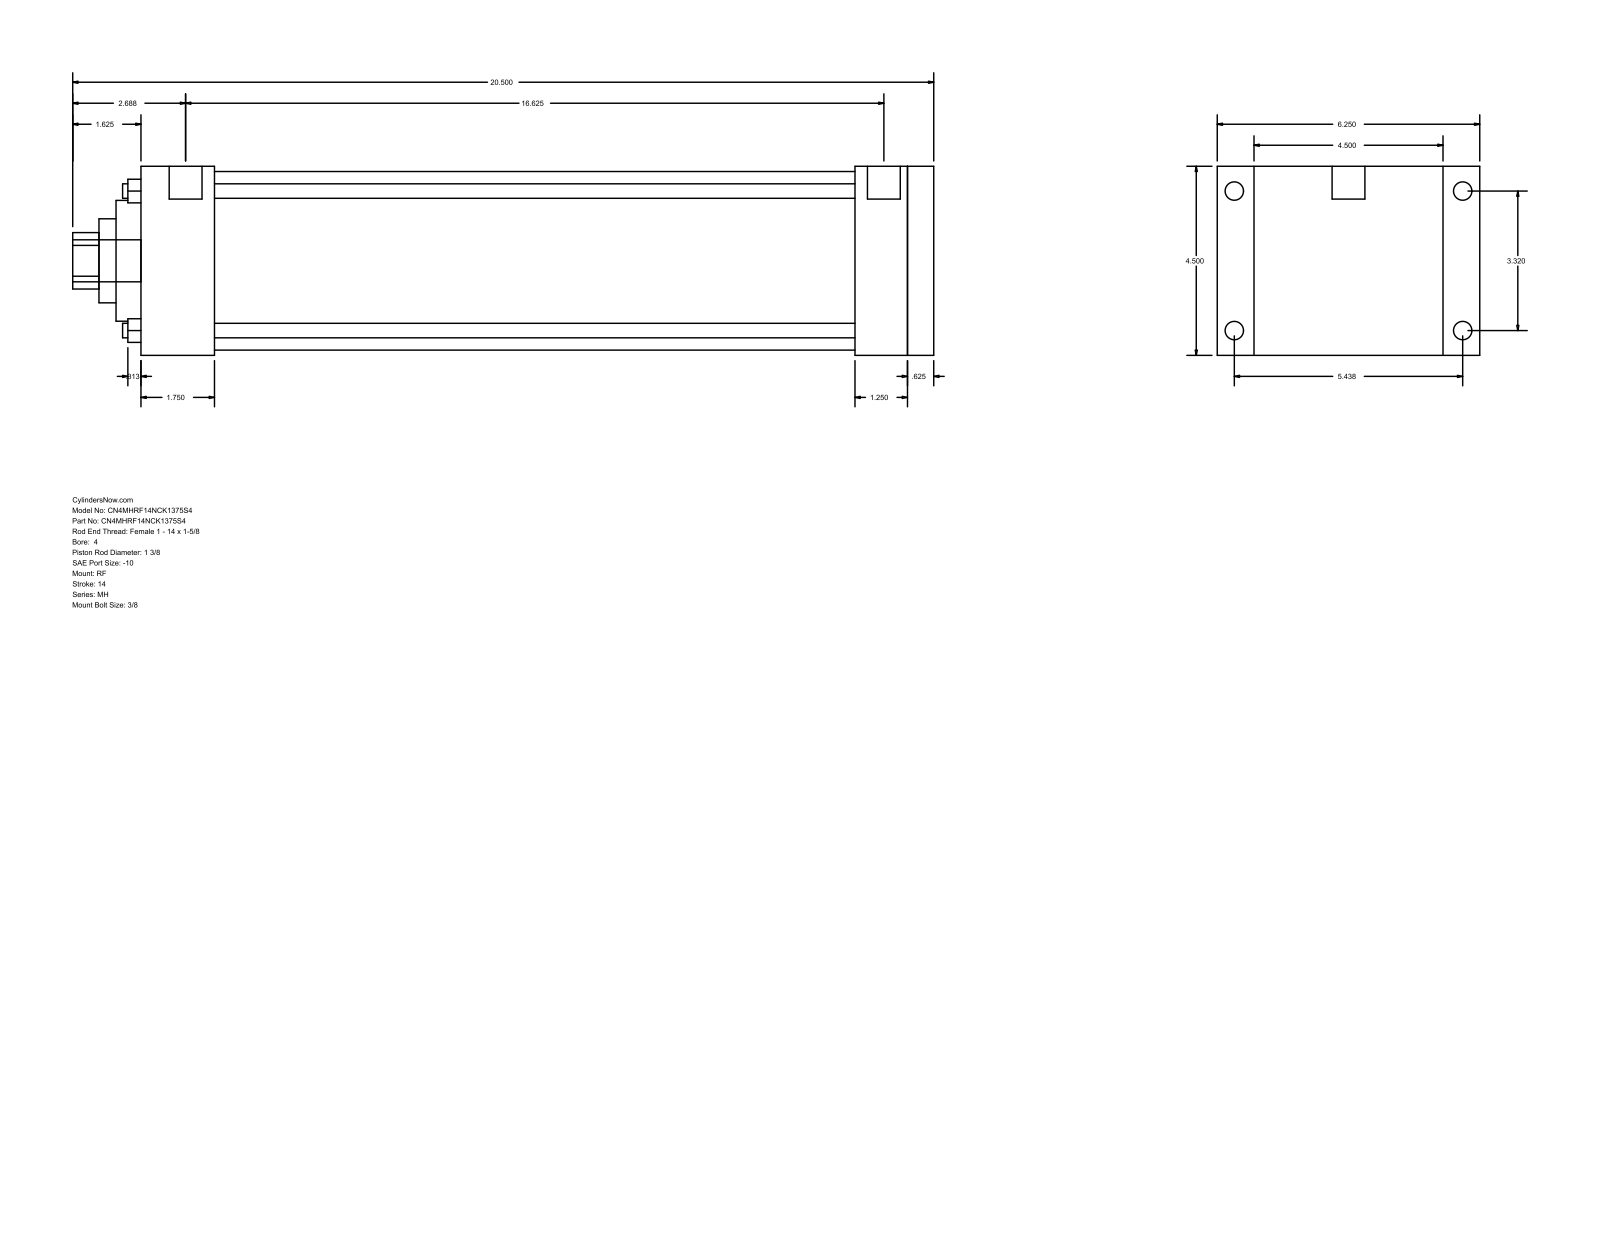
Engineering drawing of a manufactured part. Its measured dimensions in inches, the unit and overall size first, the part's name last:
Units: inches
Overall size (bounding box): 20.5 × 6.25 × 4.5
Round holes (diameter × count): ⌀0.345 ×4, ⌀1.375 ×1, ⌀2 ×1, ⌀2.875 ×1, ⌀4.25 ×1
Round bosses / shafts (diameter × count): ⌀0.438 ×4, ⌀0.344 ×4, ⌀0.781 ×2, ⌀1 ×1
Partial cylindrical surfaces — rounded edges, fillets, slot ends (radius × count): R0.672 ×1
Main face-to-face distances: 4.5, 18.875, 0.625, 18.25, 1.75, 16.5, 17.125, 17, 15.25, 1.25
Hole centre spacings: 2.347, 3.32, 4.695
Bodies: 0 solids, 94 faces (65 planar, 29 cylindrical, 0 other)
Part name (STEP PRODUCT): MH_RF__0400_1.375
STEP written by: GSSL Pune (CONFIG_CONTROL_DESIGN)
